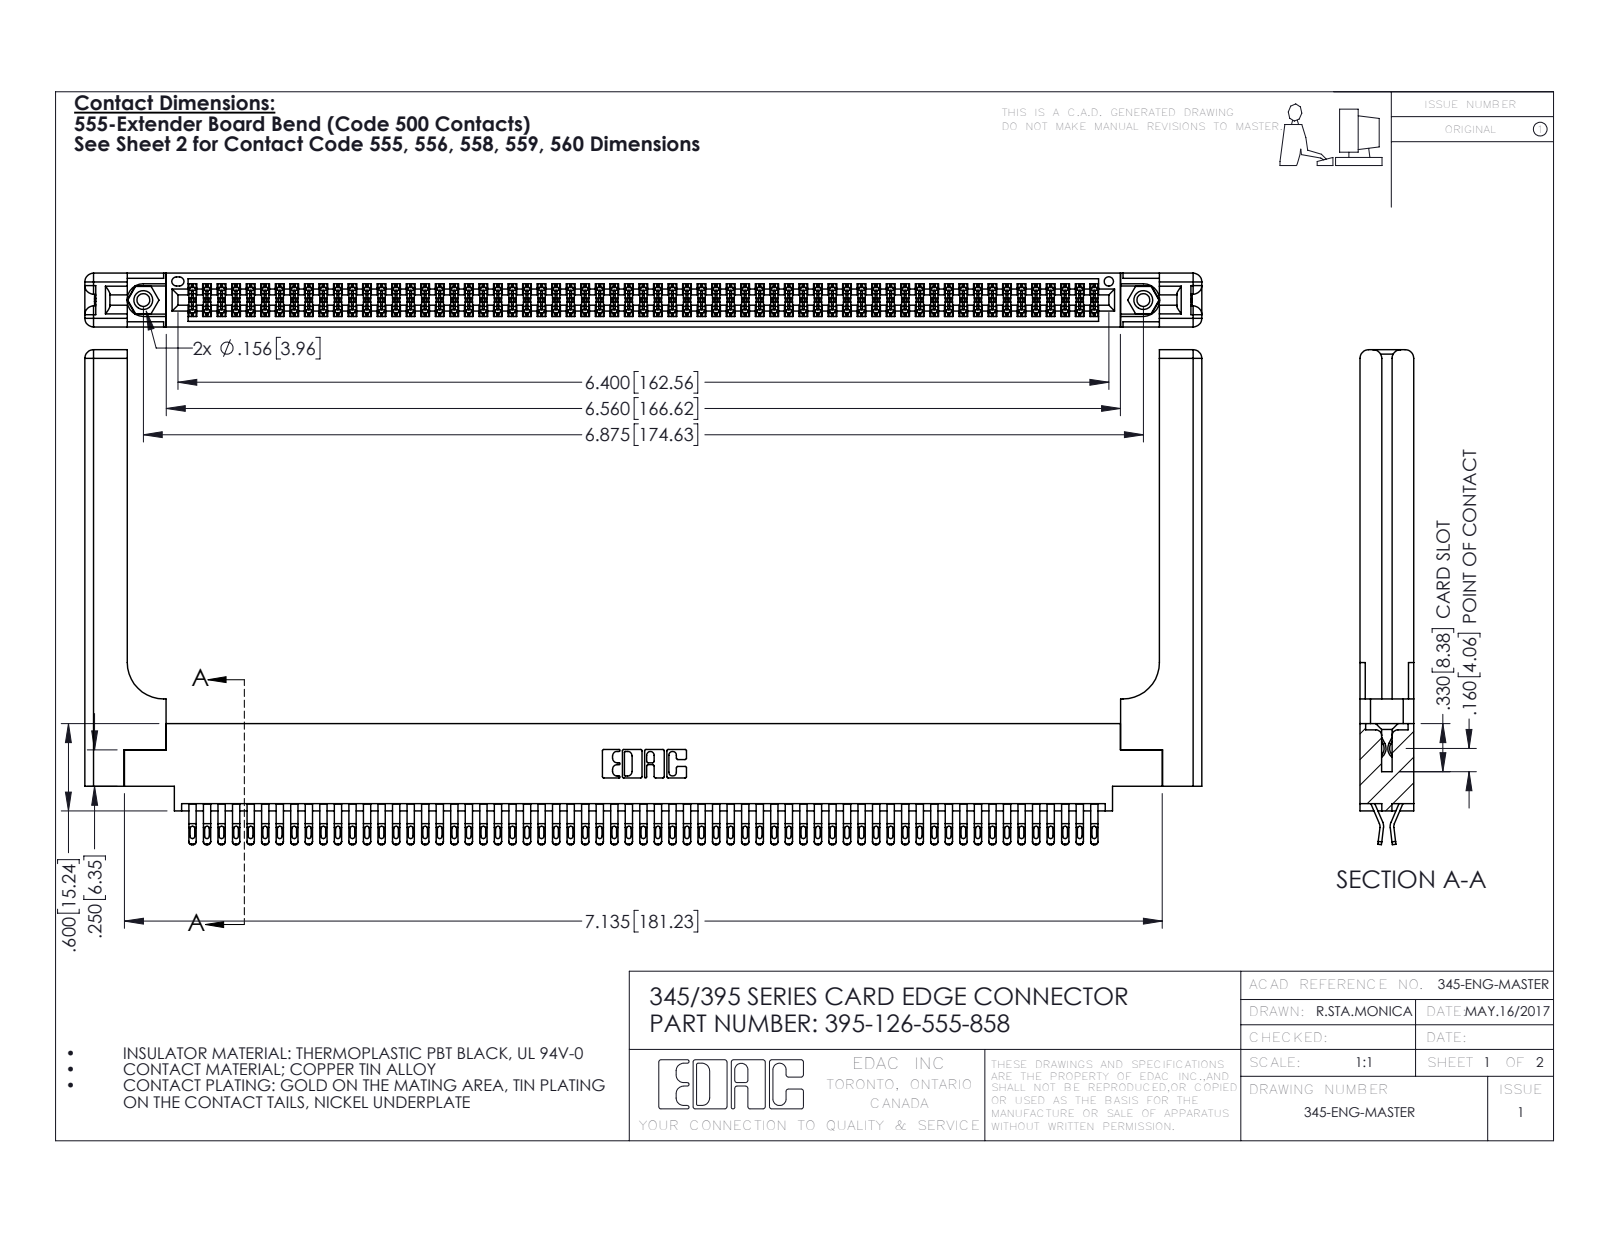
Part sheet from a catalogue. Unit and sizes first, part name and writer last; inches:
Units: inches
Overall size (bounding box): 7.679 × 3.402 × 0.37
Round holes (diameter × count): ⌀0.089 ×2, ⌀0.125 ×2, ⌀0.156 ×2, ⌀0.064 ×1
Round bosses / shafts (diameter × count): ⌀0.155 ×2
Partial cylindrical surfaces — rounded edges, fillets, slot ends (radius × count): R0.016 ×315, R0.02 ×252, R0.006 ×189, R0.01 ×22, R0.06 ×16, R0.007 ×6, R0.031 ×6, R0.026 ×3
Main face-to-face distances: 0.072, 0.298, 0.37, 0.025, 0.098, 0.272, 0.2, 0.225, 0.175, 0.148
Hole centre spacings: 0.27, 6.639, 6.875
Volume: 1.701 in³ · Surface area: 55.1 in²
Bodies: 131 solids, 7442 faces (4138 planar, 3244 cylindrical, 60 other)
Part name (STEP PRODUCT): 345 Part_0.170 Offset - 0.156 Dia-TH; 345-250-001_345-250-001-102; 345-292-001_555 Tail; 345-220-058_345-220-058 (+1 more)
STEP written by: SolidWorks 2016 (CONFIG_CONTROL_DESIGN)
